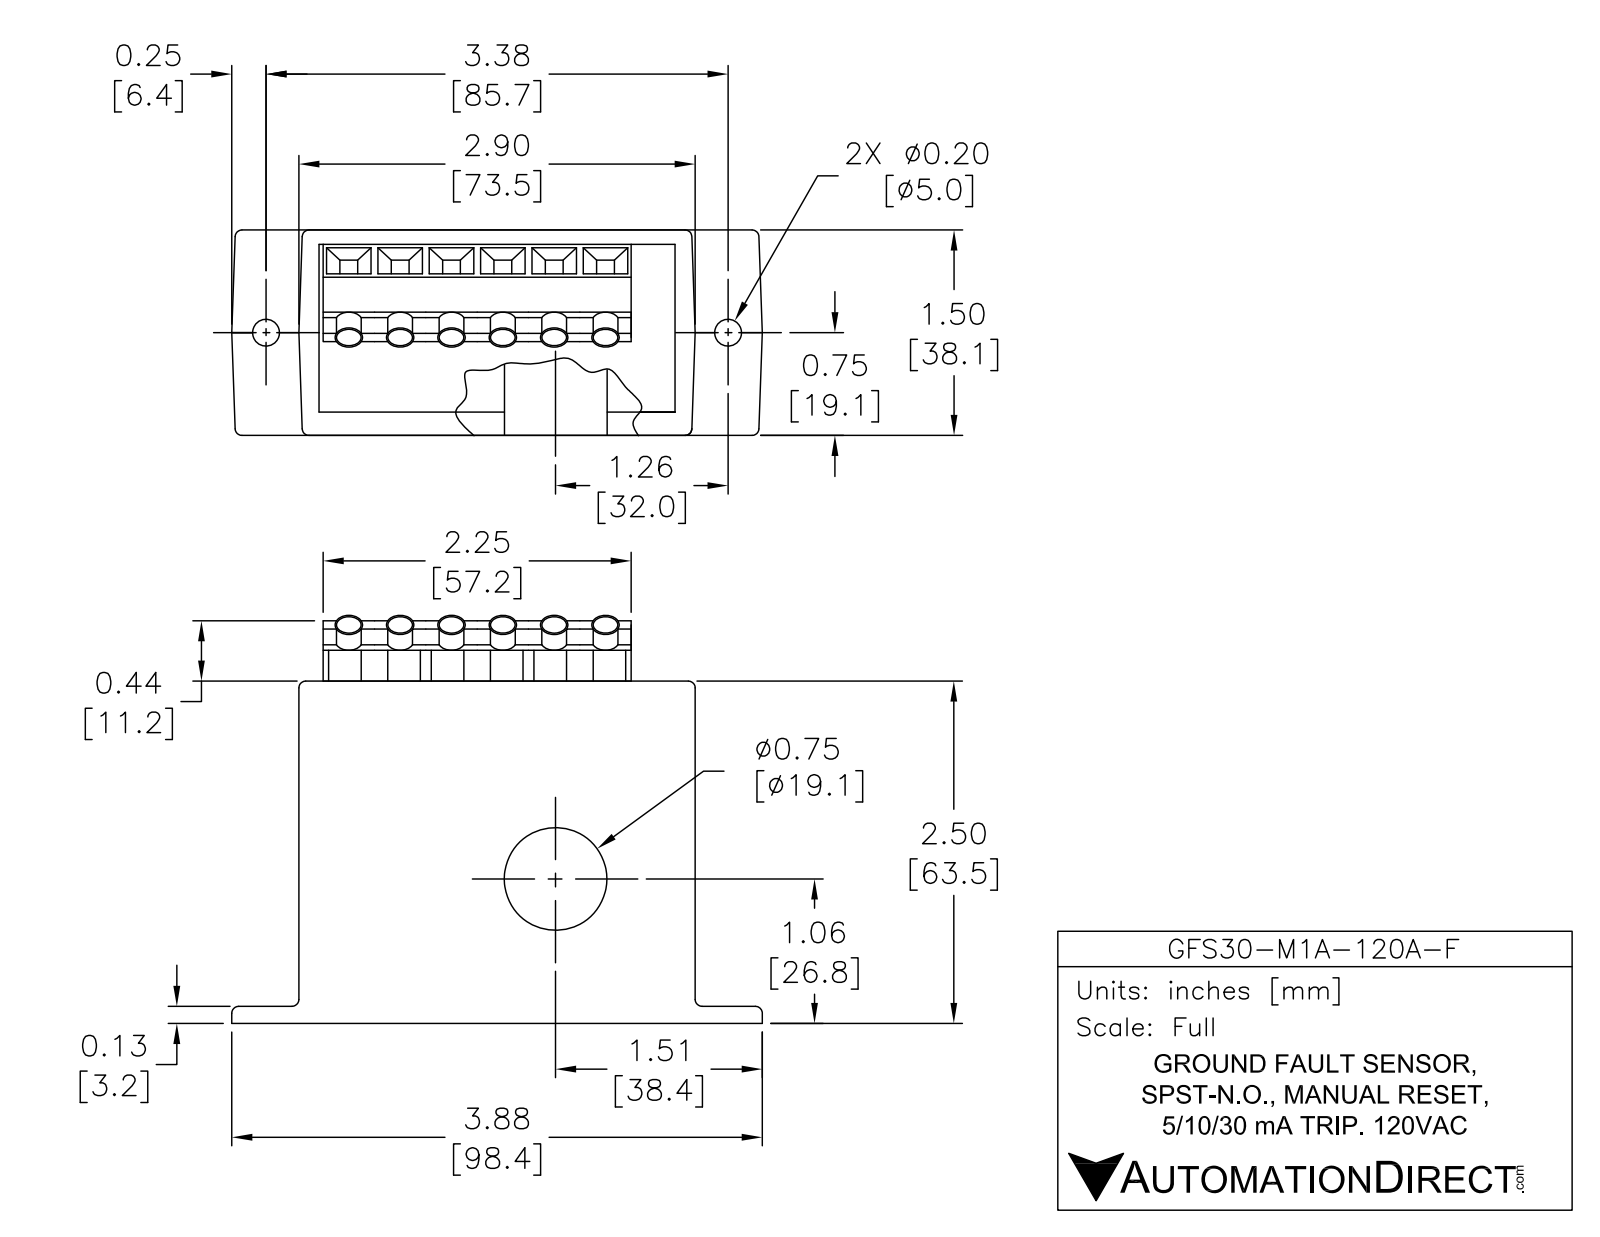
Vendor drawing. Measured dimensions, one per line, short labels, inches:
name: GFS30-M1A-120A-F
written by: SolidWorks 2019 (AUTOMOTIVE_DESIGN)
unit: in
bodies: 19 solids, 312 faces (252 planar, 56 cylindrical, 4 other)
size: 3.875 × 2.908 × 1.504
volume: 10.56 in³; area: 54.48 in²
holes: 6× ⌀0.206, 2× ⌀0.196, 2× ⌀0.2, 1× ⌀0.75
bosses: 6× ⌀0.186
rounds: 6× R0.128
face distances: 1.5, 2.895, 0.1, 2.455, 2.355, 1.504, 0.104, 2.459, 0.045, 2.334
hole spacings: 0.748, 0.354, 0.394, 0.37, 0.374, 0.681, 0.768, 1.022
